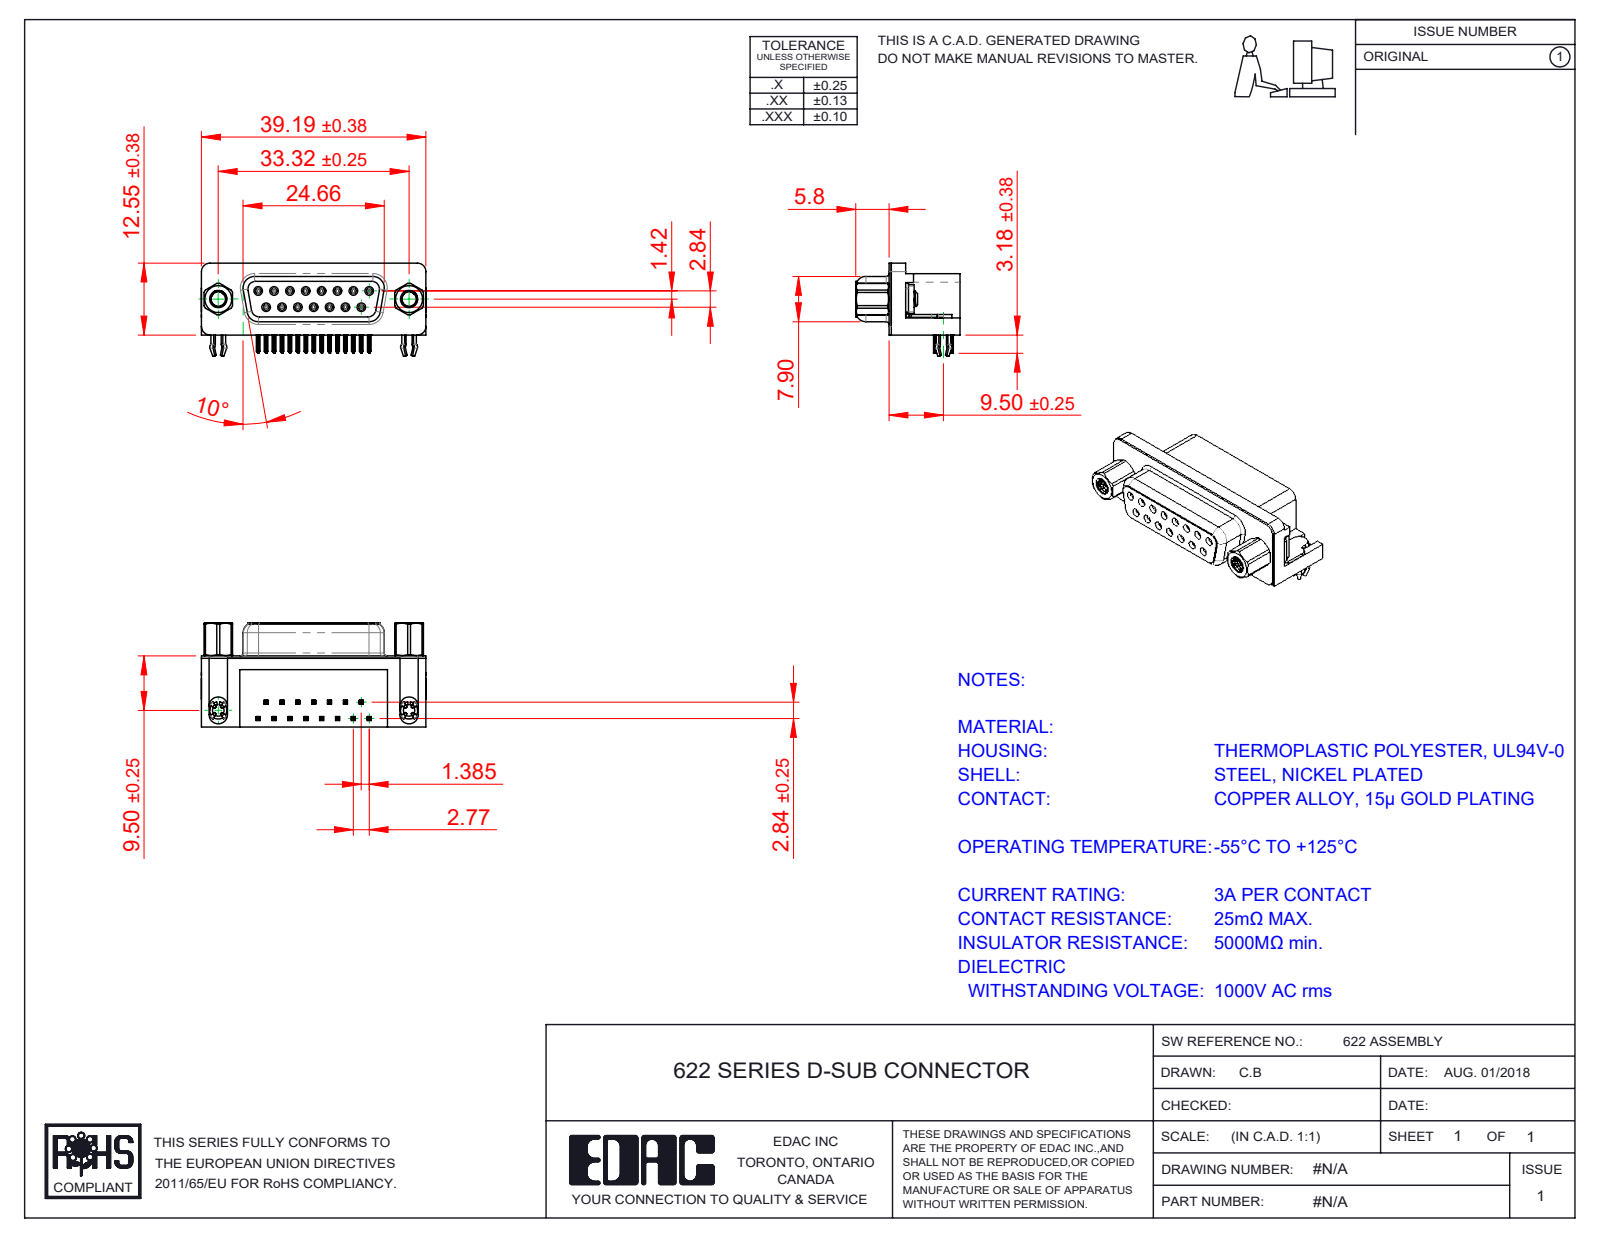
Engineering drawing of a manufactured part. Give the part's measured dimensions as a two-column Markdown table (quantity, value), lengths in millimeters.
| quantity | value |
| --- | --- |
| part name | 622-015-368-556; 622 Socket Bottom; 622 Housing_15 Socket; 622 M3 Threaded Rivet (+3 more) |
| STEP written by | SolidWorks 2016 (CONFIG_CONTROL_DESIGN) |
| units | millimeters |
| bodies | 21 solids, 2457 faces (1074 planar, 621 cylindrical, 762 other) |
| overall size | 39.22 × 18.2 × 15.73 |
| volume | 5 194 mm³ |
| surface area | 6 798 mm² |
| round holes (diameter × count) | 0.8 × 15, 0.9 × 15, 2.26 × 2, 2.5 × 2, 4 × 2, 4.8 × 2, 5 × 2 |
| round bosses / shafts (diameter × count) | 1.2 × 15, 4.9 × 2, 4.75 × 2, 3.9 × 2, 3.26 × 2 |
| partial cylindrical surfaces (radius × count) | 0.1 × 120, 0.15 × 60, 0.35 × 30, 1 × 18, 0.34 × 15, 0.25 × 8, 1.35 × 8, 1.5 × 8 |
| main face-to-face distances | 0.4, 12, 6.2, 12.4, 10.35, 2.9, 6.65, 0.85, 0.35, 5.8 |
| hole center spacings | 3.16, 2.77, 5.54, 8.31, 11.08, 5.03, 5.04, 7.48 |
